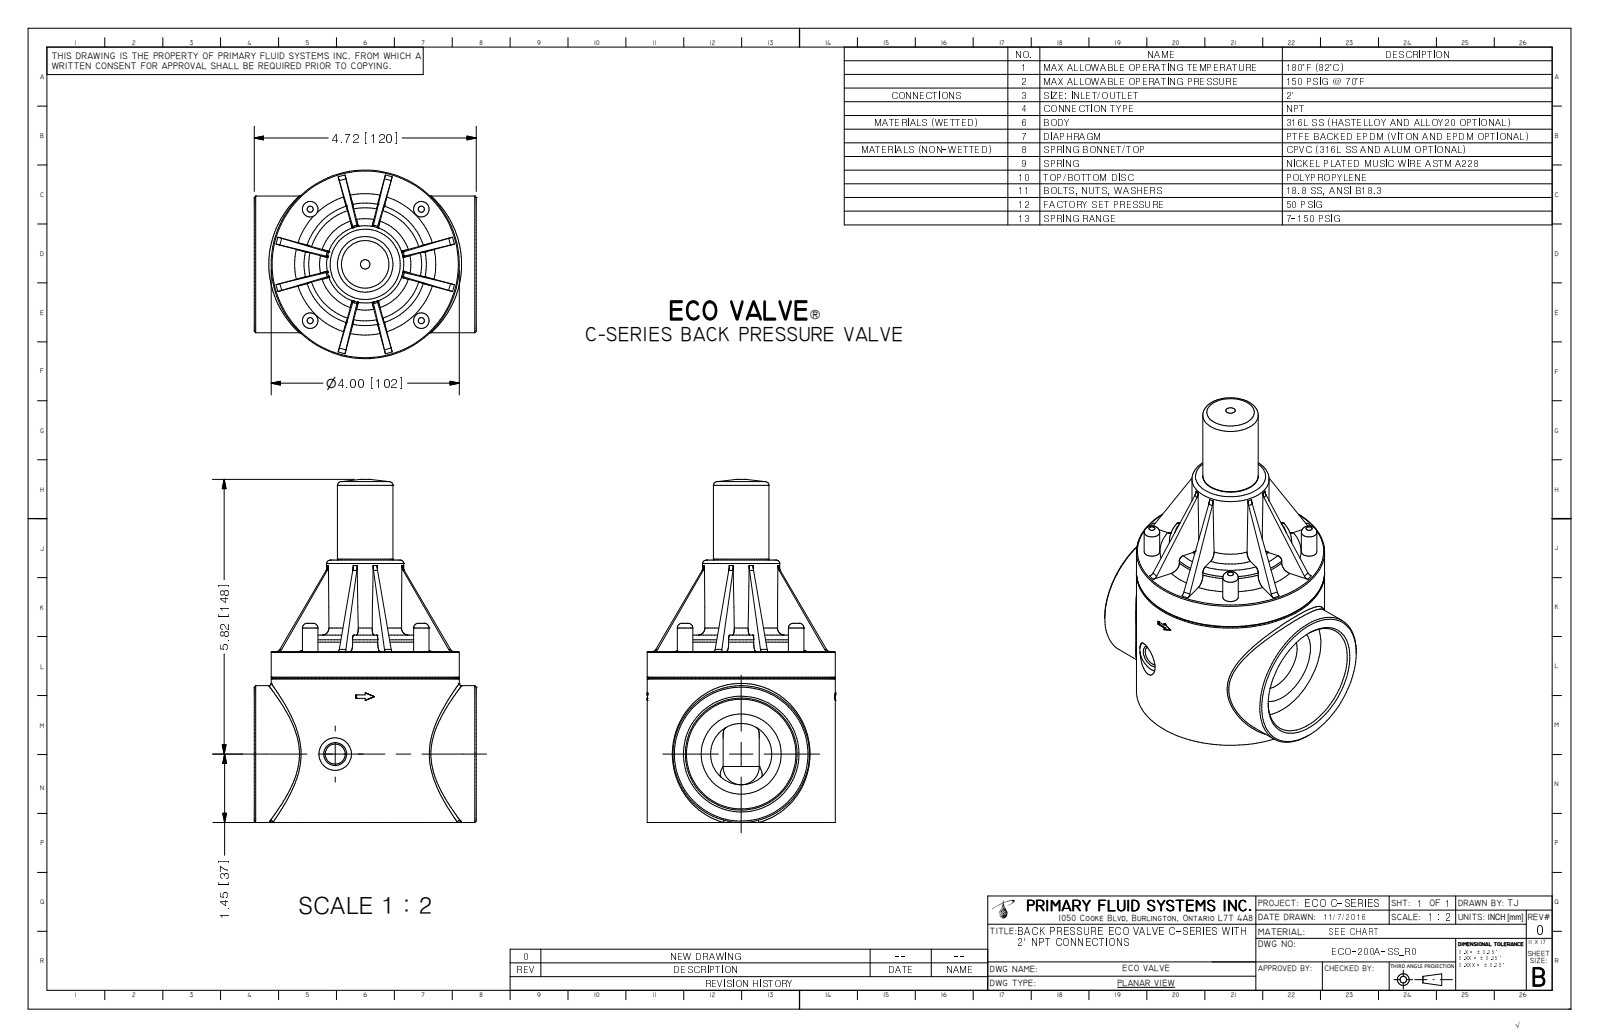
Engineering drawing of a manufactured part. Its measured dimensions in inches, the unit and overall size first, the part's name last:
Units: inches
Overall size (bounding box): 7.274 × 4.72 × 4
Round holes (diameter × count): ⌀0.23 ×4, ⌀0.257 ×1, ⌀0.426 ×1, ⌀0.691 ×1
Round bosses / shafts (diameter × count): ⌀0.33 ×4, ⌀4 ×1, ⌀2.9 ×1, ⌀2.6 ×1, ⌀1.64 ×1, ⌀1.18 ×1, ⌀0.256 ×1
Partial cylindrical surfaces — rounded edges, fillets, slot ends (radius × count): R0.1 ×8, R0.128 ×7, R0.2 ×6, R0.129 ×3, R1.98 ×1
Main face-to-face distances: 3.624, 3.106, 0.807, 3.913, 4.72, 0.35, 3.974, 5.564, 1.94, 1.59
Hole centre spacings: 2.363, 2.363, 3.342, 3.341
Volume: 52.82 in³ · Surface area: 139.1 in²
Bodies: 1 solid, 228 faces (102 planar, 53 cylindrical, 73 other)
Part name (STEP PRODUCT): ECO-200A-SS_R0
STEP written by: Autodesk Inventor 2009 (AUTOMOTIVE_DESIGN)
